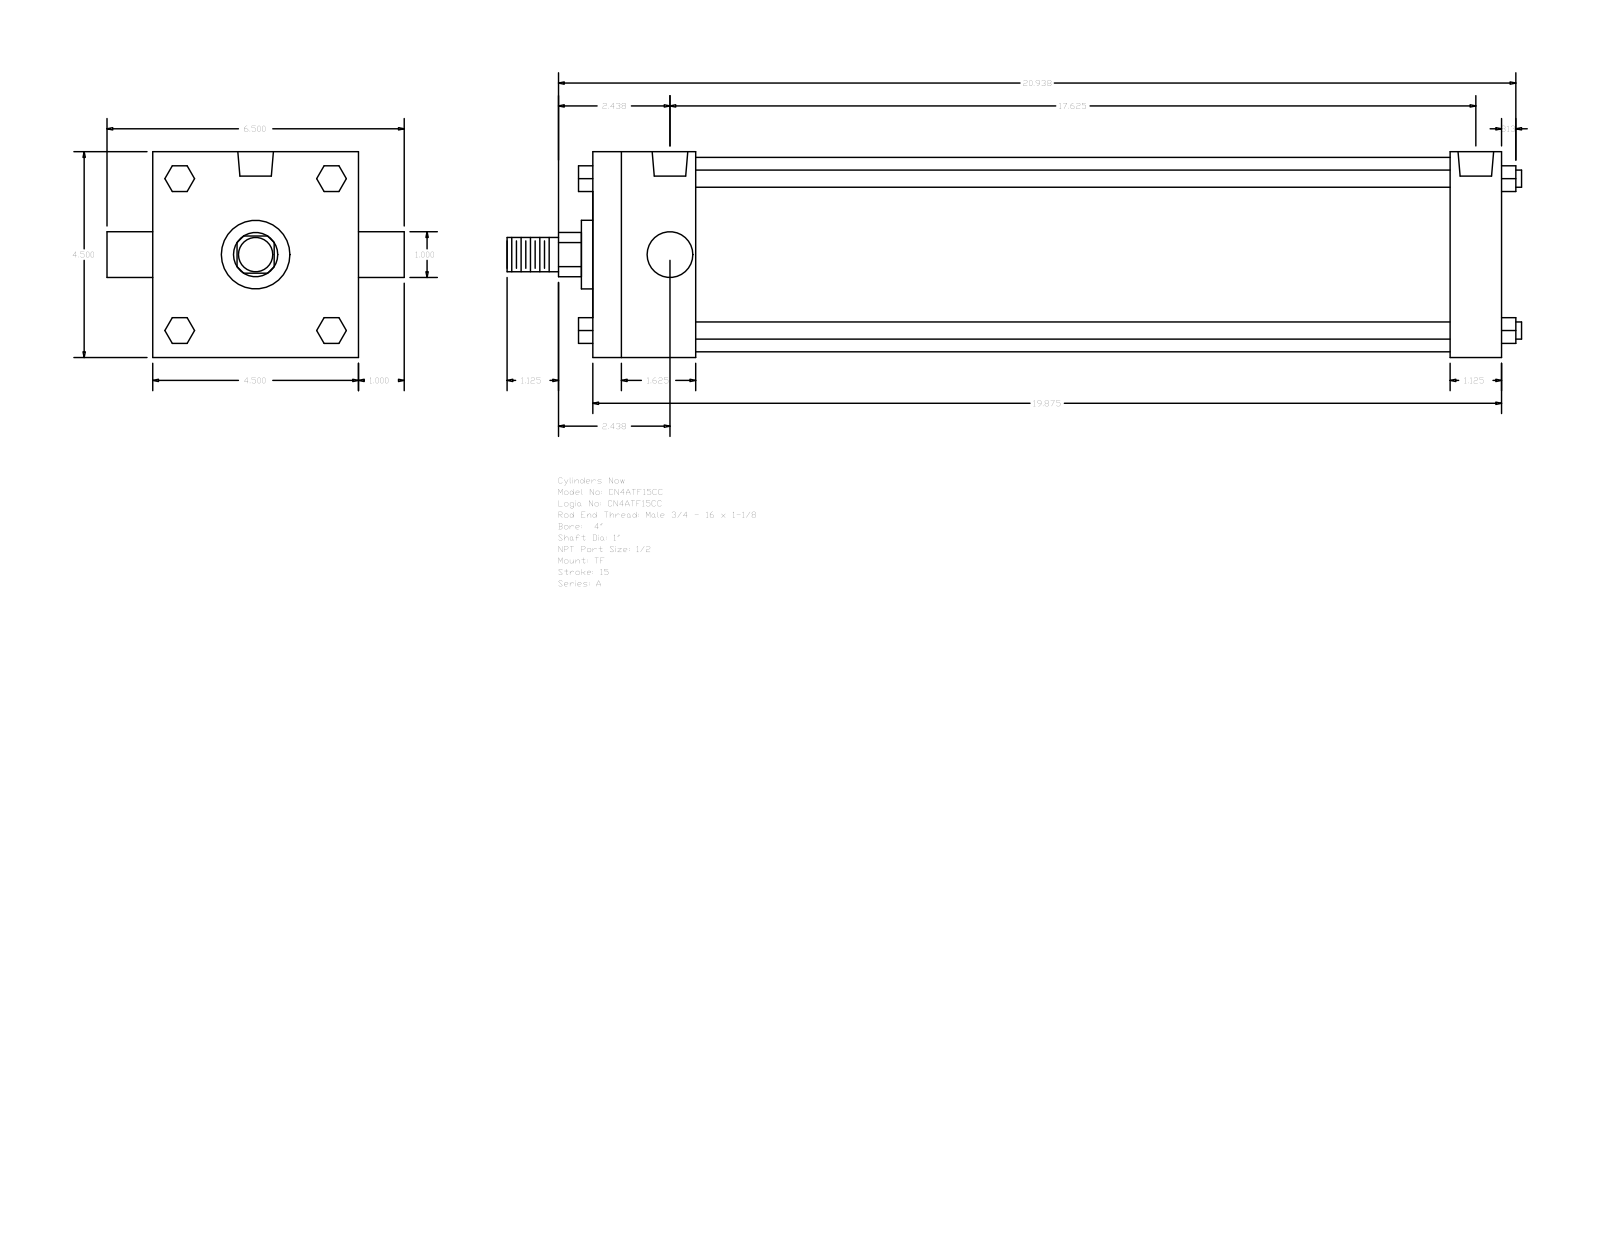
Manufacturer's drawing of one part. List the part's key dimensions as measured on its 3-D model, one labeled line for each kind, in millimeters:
Part name (STEP PRODUCT): A_TF__0400_1
STEP written by: GSSL Pune (CONFIG_CONTROL_DESIGN)
Units: millimetres
Bodies: 0 solids, 120 faces (92 planar, 28 cylindrical, 0 other)
Overall size (bounding box): 563.56 × 165.1 × 114.3
Round holes (diameter × count): ⌀8.73 ×3, ⌀19.77 ×2
Round bosses / shafts (diameter × count): ⌀9.53 ×4, ⌀25.4 ×2, ⌀107.95 ×1, ⌀38.1 ×1, ⌀19.05 ×1
Partial cylindrical surfaces — rounded edges, fillets, slot ends (radius × count): R12.29 ×1
Main face-to-face distances: 114.3, 504.83, 476.25, 28.58, 57.15, 419.1, 447.68, 14.29, 42.16, 73.03
Hole centre spacings: 3.18, 444.5, 441.32, 447.68
